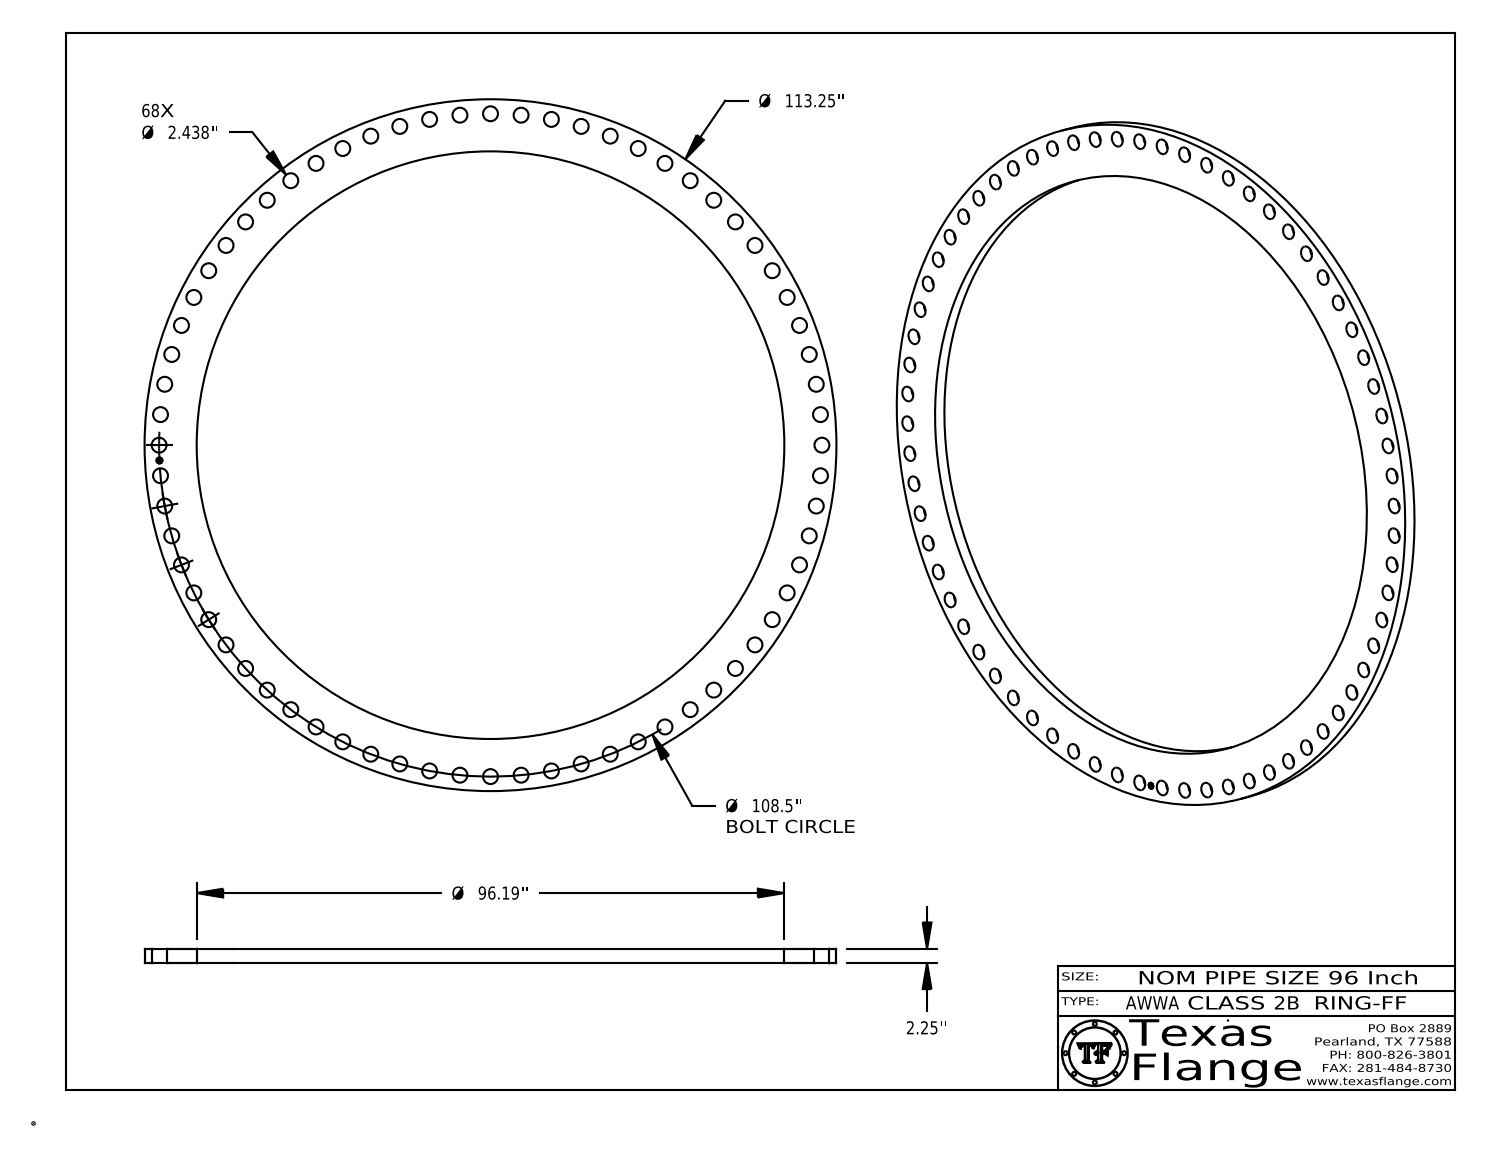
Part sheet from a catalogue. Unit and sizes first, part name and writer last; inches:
Units: inches
Overall size (bounding box): 113.25 × 113.25 × 2.25
Round holes (diameter × count): ⌀2.438 ×68, ⌀1 ×1, ⌀96.19 ×1
Round bosses / shafts (diameter × count): ⌀0.061 ×8, ⌀113.25 ×1, ⌀0.788 ×1
Main face-to-face distances: 2.25, 2.235, 0.015, 0.298, 0.293, 0.054, 0.193, 0.248, 0.044, 0.15
Hole centre spacings: 54.25, 29.693, 5.011, 10.011, 14.99, 19.937, 39.195, 43.826
Volume: 5 600 in³ · Surface area: 7 630 in²
Bodies: 1 solid, 527 faces (367 planar, 160 cylindrical, 0 other)
Part name (STEP PRODUCT): AWWA Class 2B-RING-FF
STEP written by: CATIA V5 STEP AP214 (AUTOMOTIVE_DESIGN)
